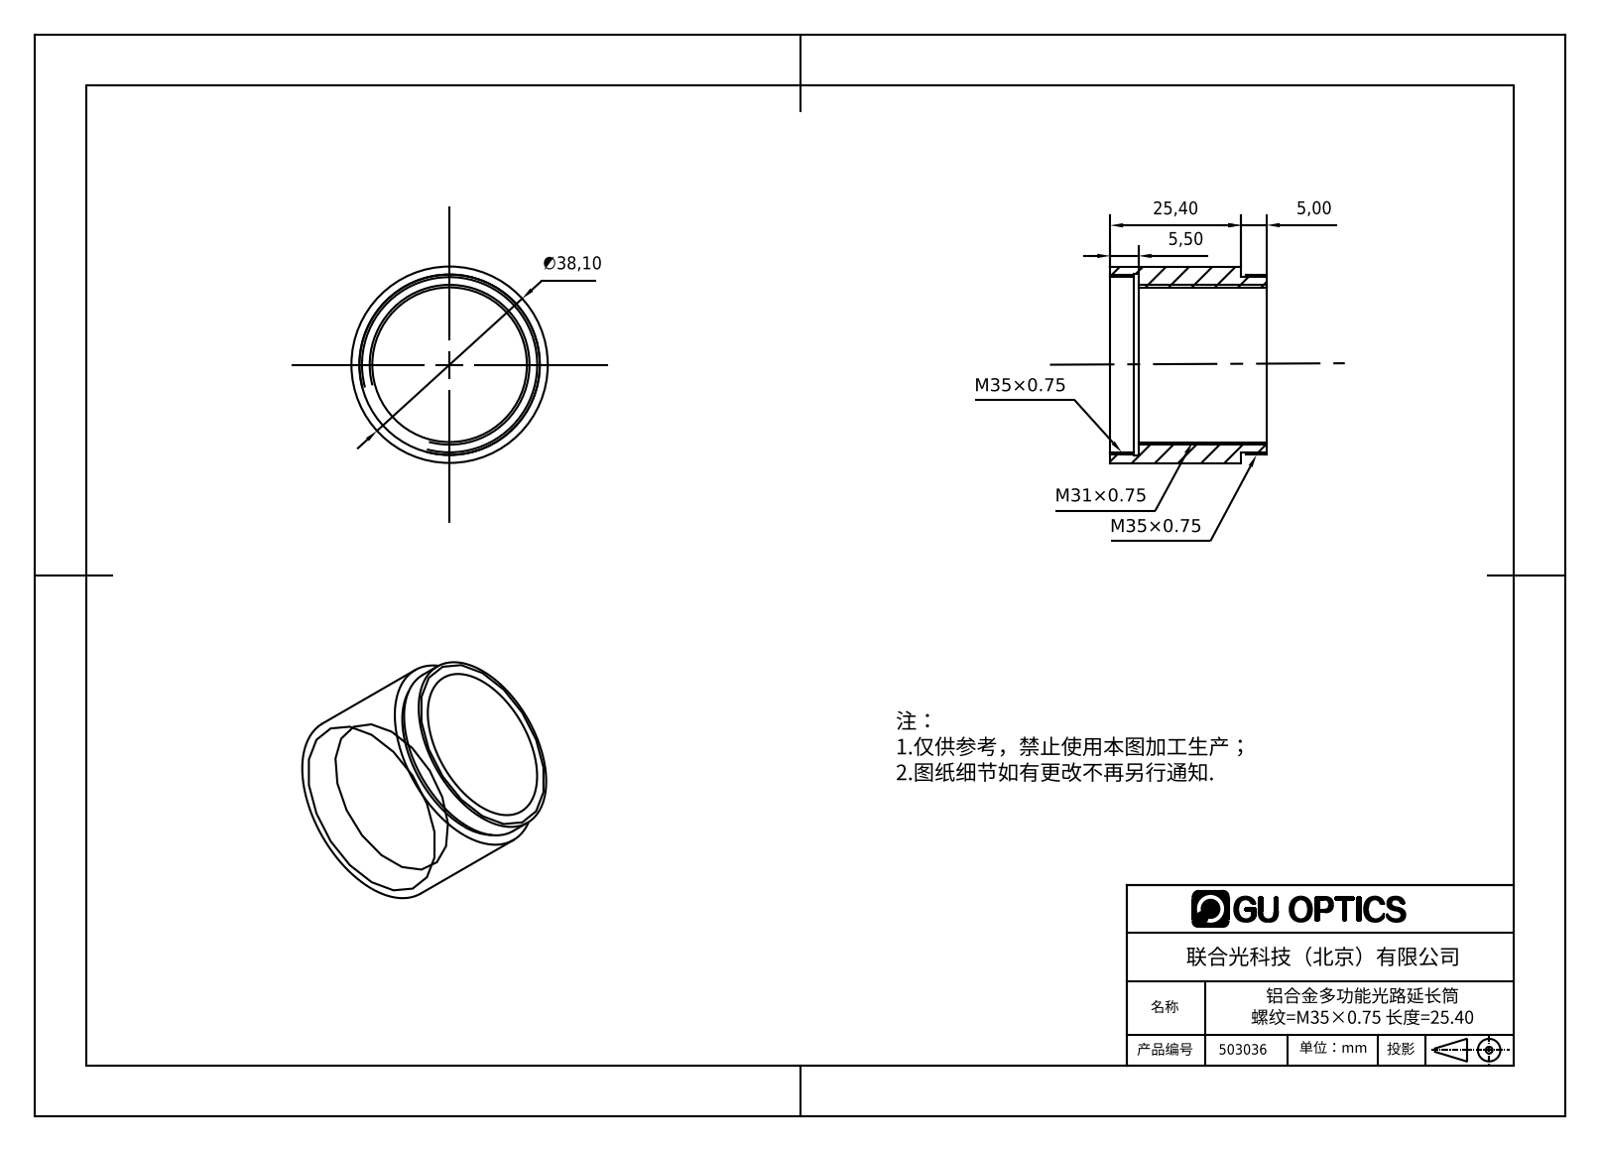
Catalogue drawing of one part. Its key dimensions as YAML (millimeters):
part_name: "503036"
step_written_by: "SolidWorks 2016 (AUTOMOTIVE_DESIGN)"
units: millimeters
bodies: {solids: 1, faces: 18, planar: 6, cylindrical: 12, other: 0}
overall_size: [38.1, 38.1, 30.4]
volume: 11055
surface_area: 7630
round_holes:
  - {diameter: 30, count: 1}
  - {diameter: 34, count: 1}
  - {diameter: 35.2, count: 1}
round_bosses_or_shafts:
  - {diameter: 38.1, count: 1}
  - {diameter: 35, count: 1}
face_to_face_distances: [24.9, 19.9, 5, 5.5, 25.4, 30.4, 1, 20.9, 4.5, 25.9]
